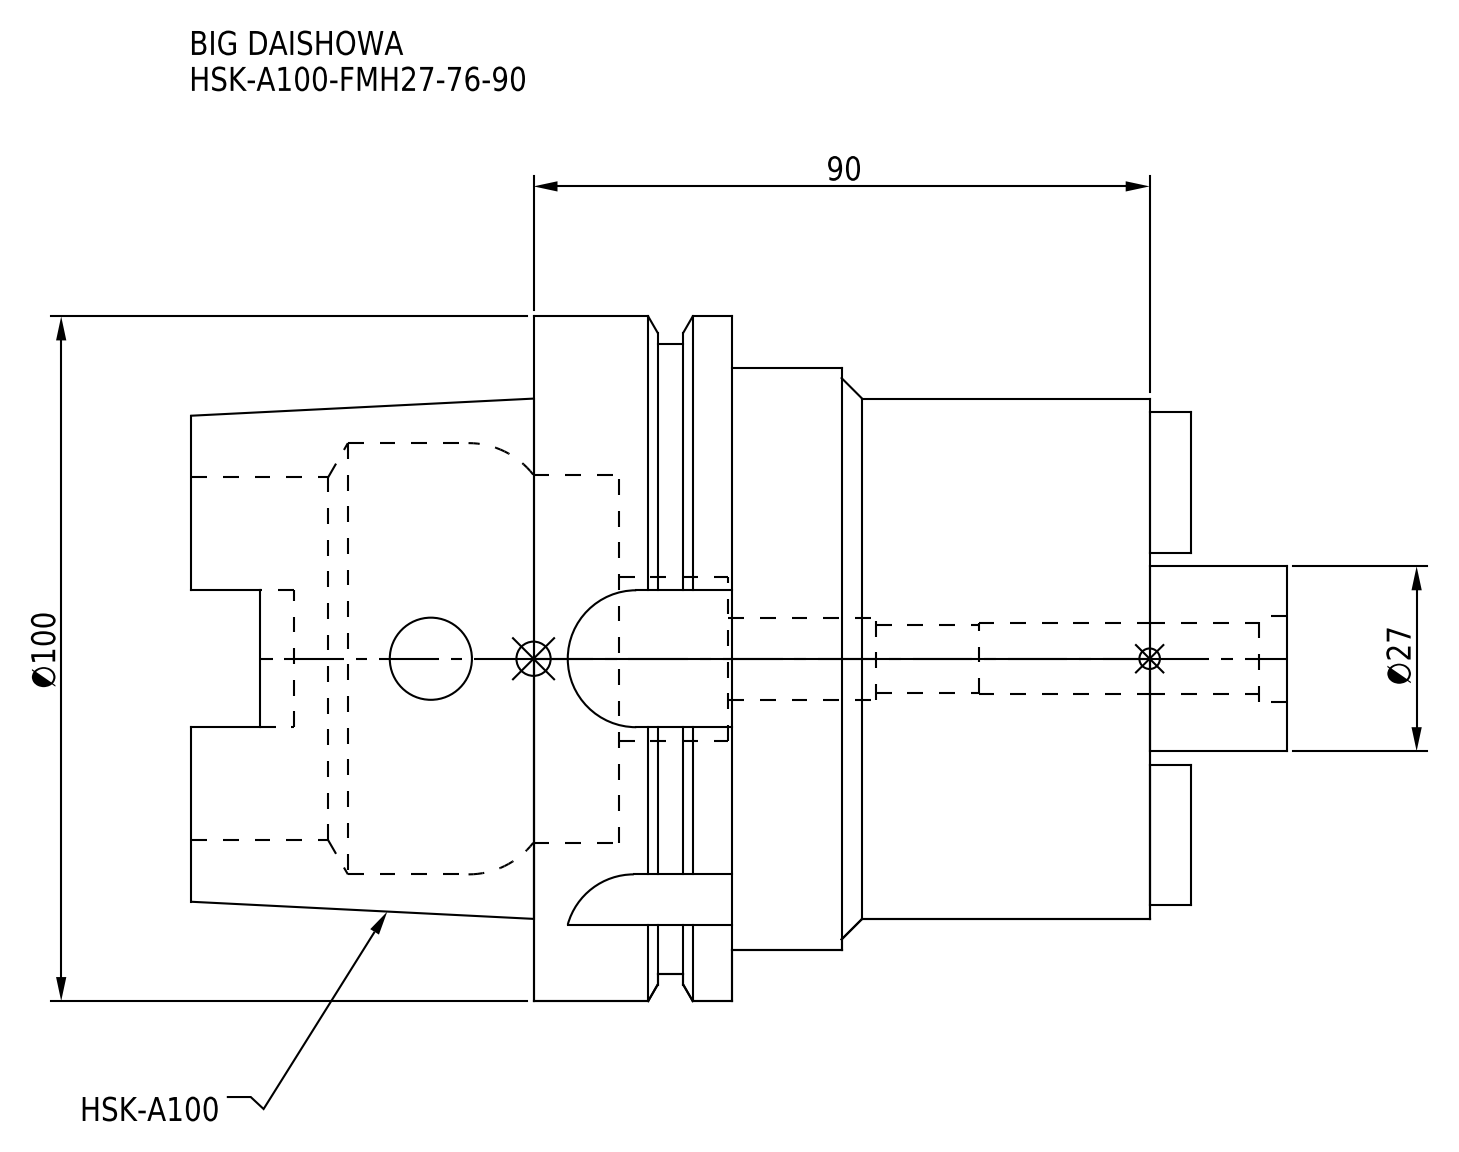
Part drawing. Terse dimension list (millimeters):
name: HSK-A100-FMH27-76-90
written by: CREO PARAMETRIC BY PTC INC, 2016380 (AUTOMOTIVE_DESIGN)
unit: mm
bodies: 1 solid, 109 faces (47 planar, 46 cylindrical, 16 other)
size: 160 × 100 × 100
volume: 556 412 mm³; area: 69 690 mm²
holes: 2× ⌀12, 1× ⌀10, 1× ⌀10.3, 1× ⌀12.5, 1× ⌀24, 1× ⌀53, 1× ⌀53.8, 1× ⌀63
bosses: 1× ⌀100, 1× ⌀92, 1× ⌀85, 1× ⌀76, 1× ⌀27
rounds: 4× R4.88, 4× R10
face distances: 90, 16.55, 61, 29, 77.55, 12.45, 50, 140, 79, 62.45
